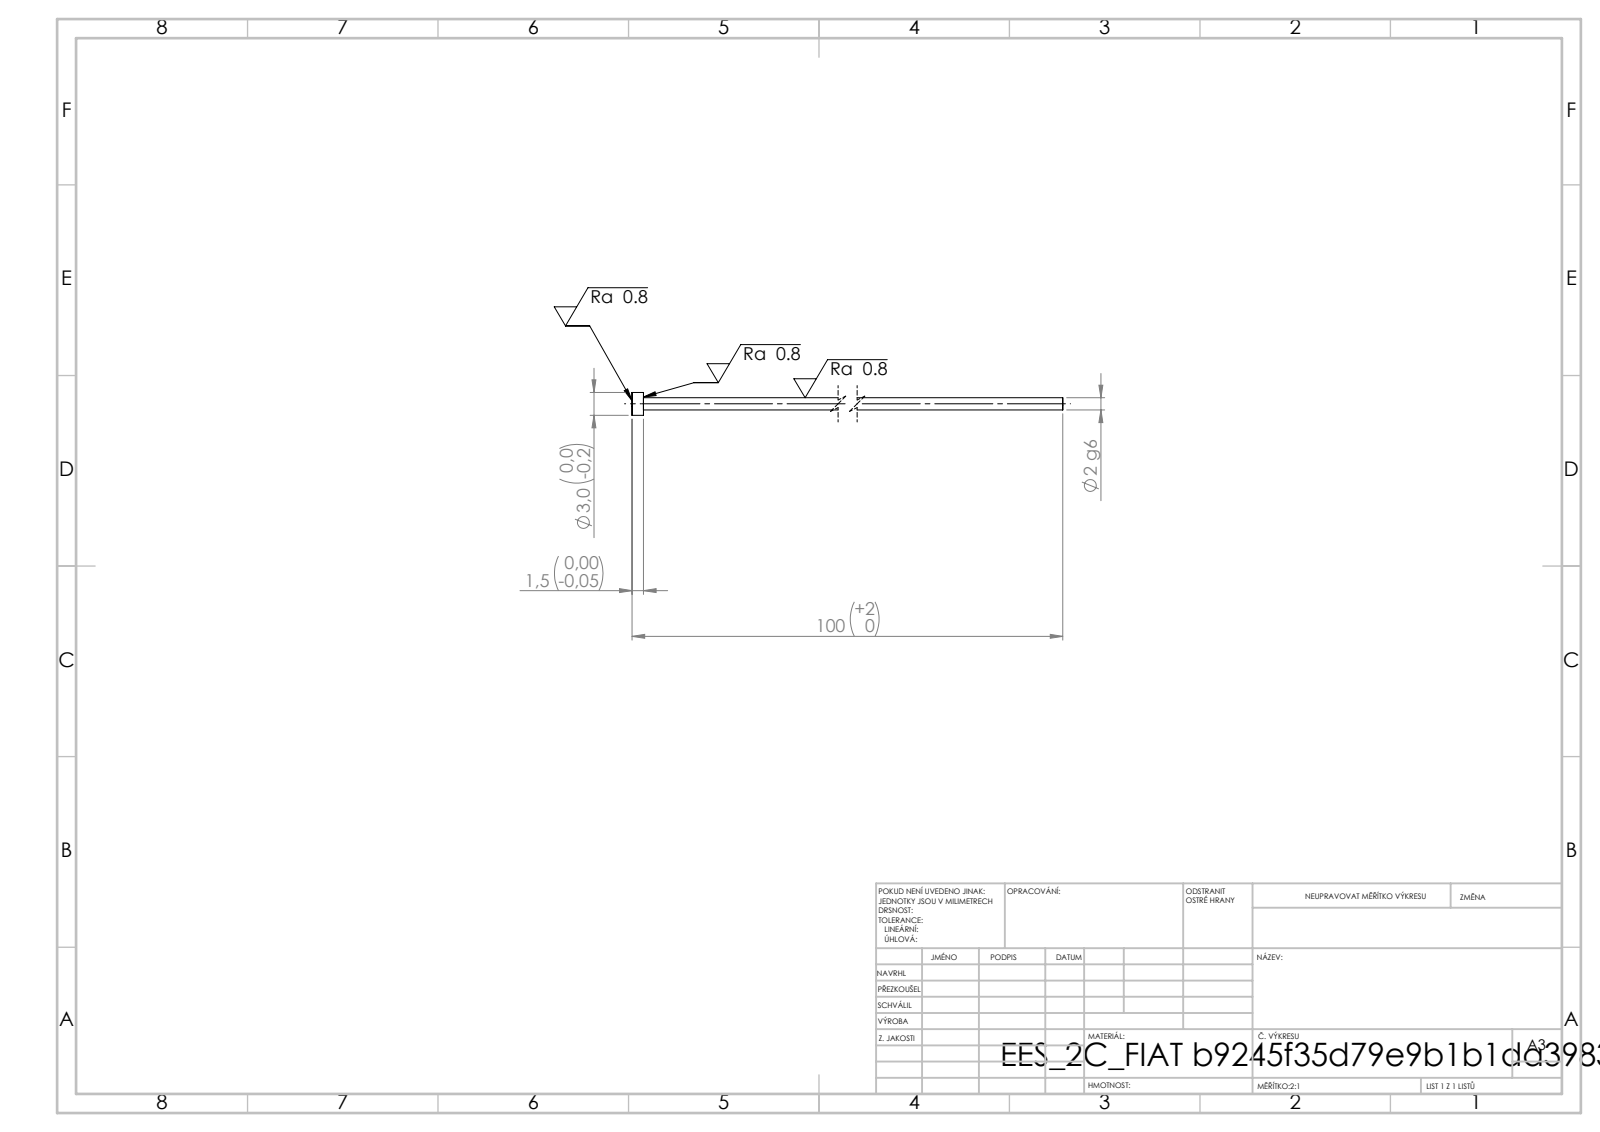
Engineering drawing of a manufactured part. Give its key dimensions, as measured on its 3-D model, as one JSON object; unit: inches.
{"step_written_by": "SolidWorks 2019 (CONFIG_CONTROL_DESIGN)", "units": "inches", "bodies": {"solids": 1, "faces": 7, "planar": 3, "cylindrical": 4, "other": 0}, "overall_size": [3.937, 0.118, 0.118], "volume_in3": 0.013, "surface_area_in2": 0.811, "round_bosses_or_shafts": [[0.118, 1], [0.063, 1]], "face_to_face_distances": [0.059, 3.937, 3.878]}
